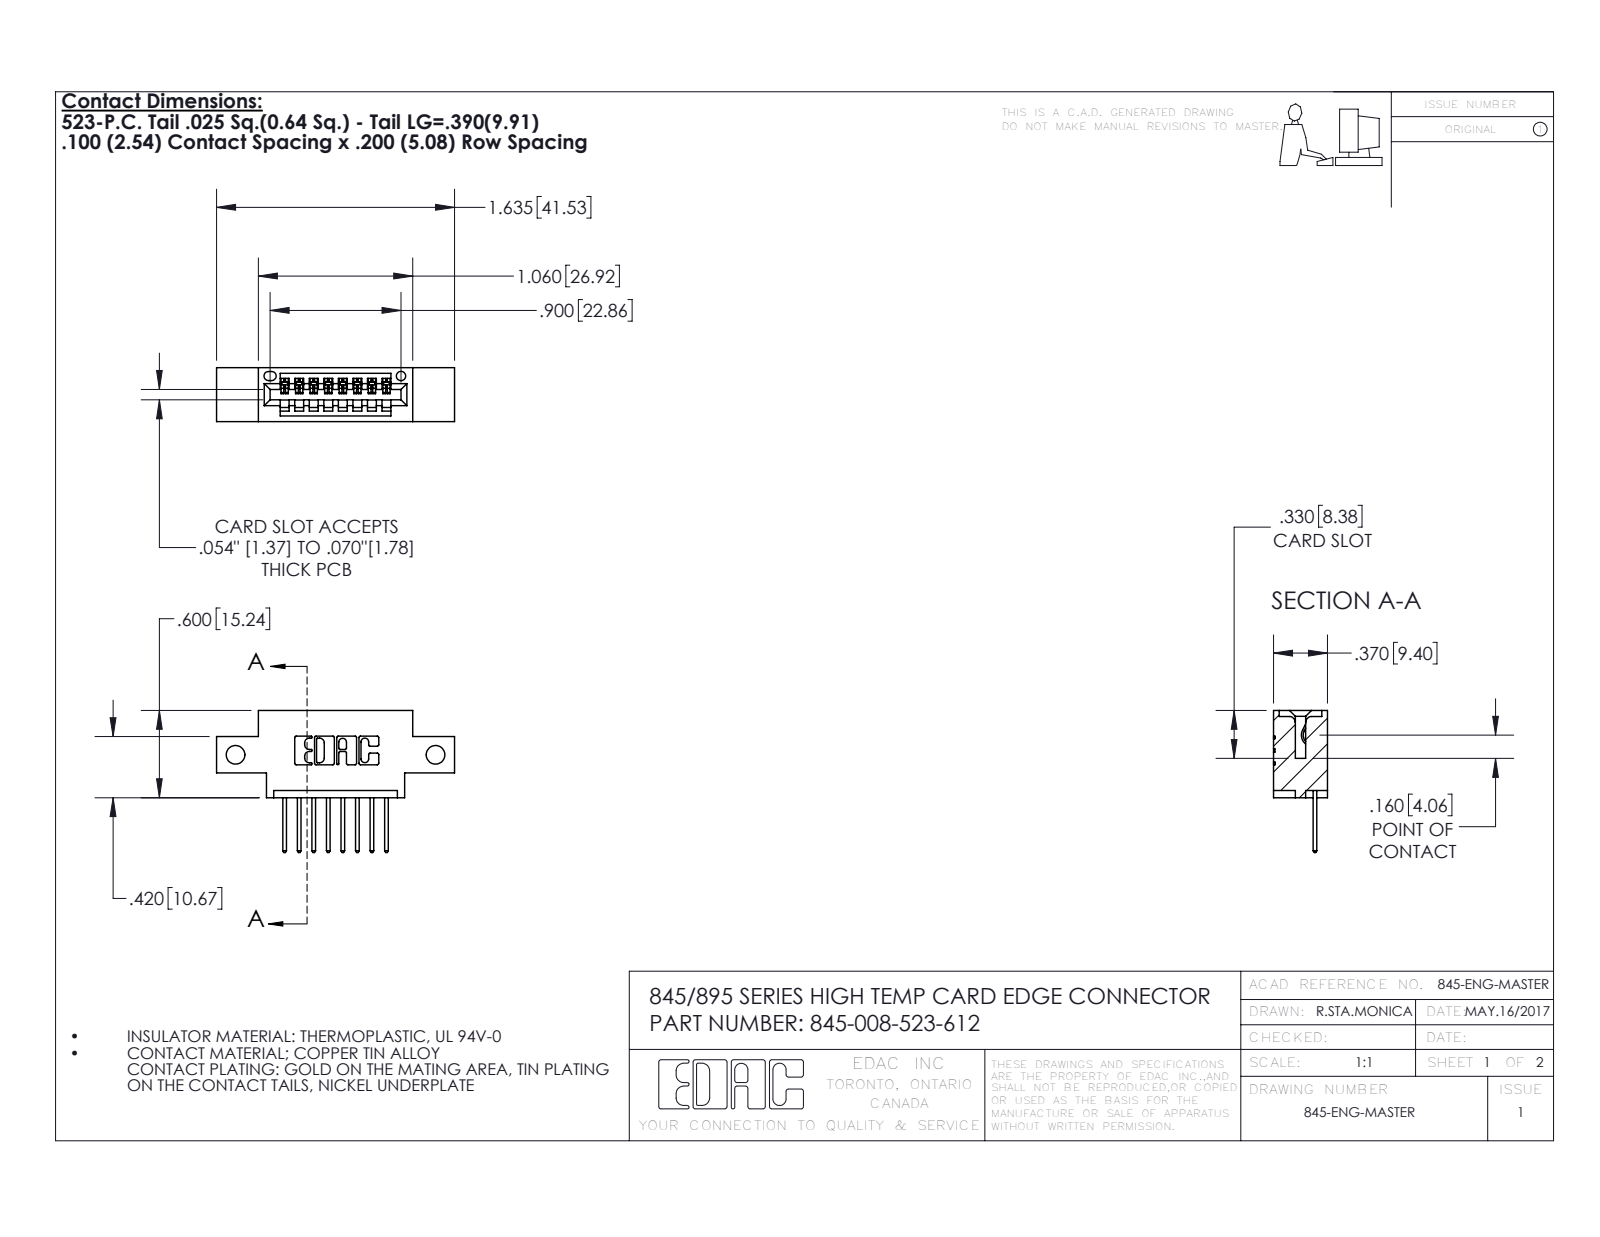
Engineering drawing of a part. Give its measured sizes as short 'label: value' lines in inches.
name: 345-292-001_345-293-123; 345-008-523-612; 345 Part_0.170 Offset - Side Mount
written by: SolidWorks 2016 (CONFIG_CONTROL_DESIGN)
unit: in
bodies: 9 solids, 594 faces (404 planar, 190 cylindrical, 0 other)
size: 1.635 × 0.977 × 0.37
volume: 0.211 in³; area: 6.405 in²
holes: 2× ⌀0.128, 1× ⌀0.064
rounds: 22× R0.01, 16× R0.006, 16× R0.01, 6× R0.007, 6× R0.031, 3× R0.026, 2× R0.031, 2× R0.04
face distances: 0.37, 0.2, 0.298, 0.072, 0.1, 0.098, 0.272, 0.025, 0.06, 0.25
hole spacings: 1.375
